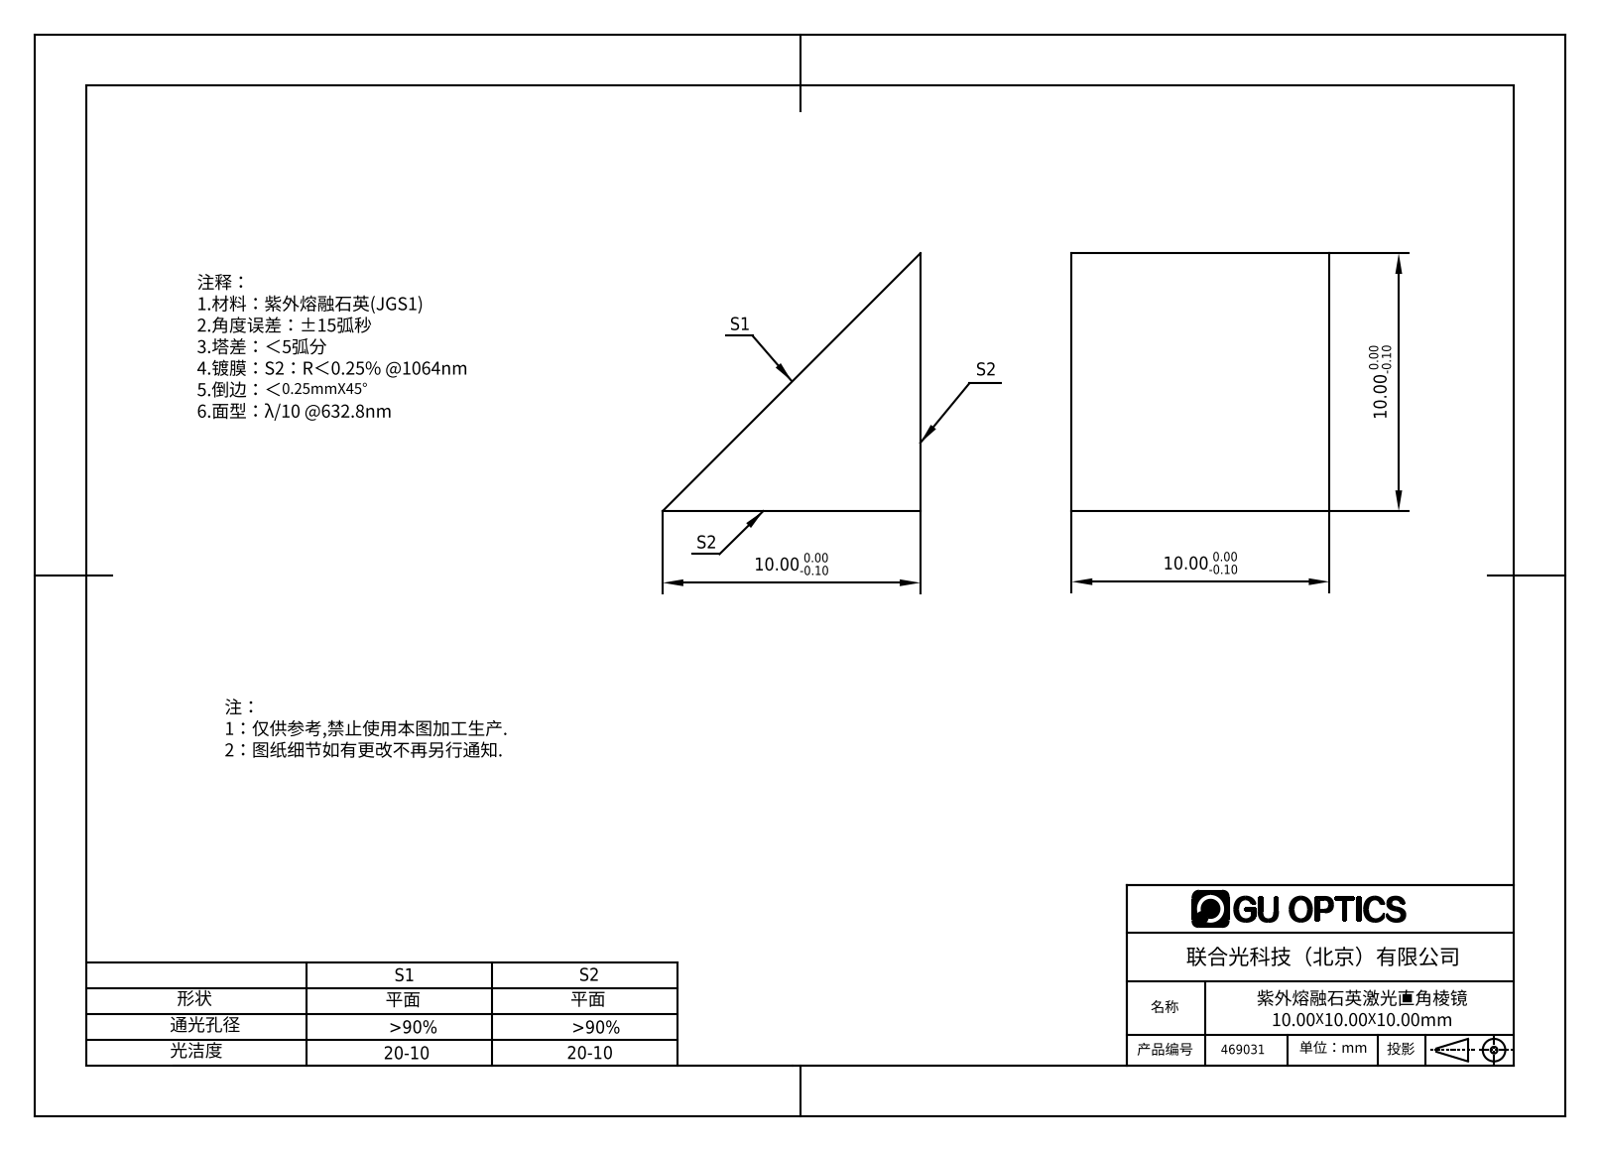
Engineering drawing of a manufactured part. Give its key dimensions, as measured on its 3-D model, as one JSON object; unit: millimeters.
{"part_name": "469001", "step_written_by": "SolidWorks 2016 (AUTOMOTIVE_DESIGN)", "units": "millimeters", "bodies": {"solids": 1, "faces": 5, "planar": 5, "cylindrical": 0, "other": 0}, "overall_size": [12.55, 10, 8.34], "volume_mm3": 489, "surface_area_mm2": 424, "face_to_face_distances": [10]}
